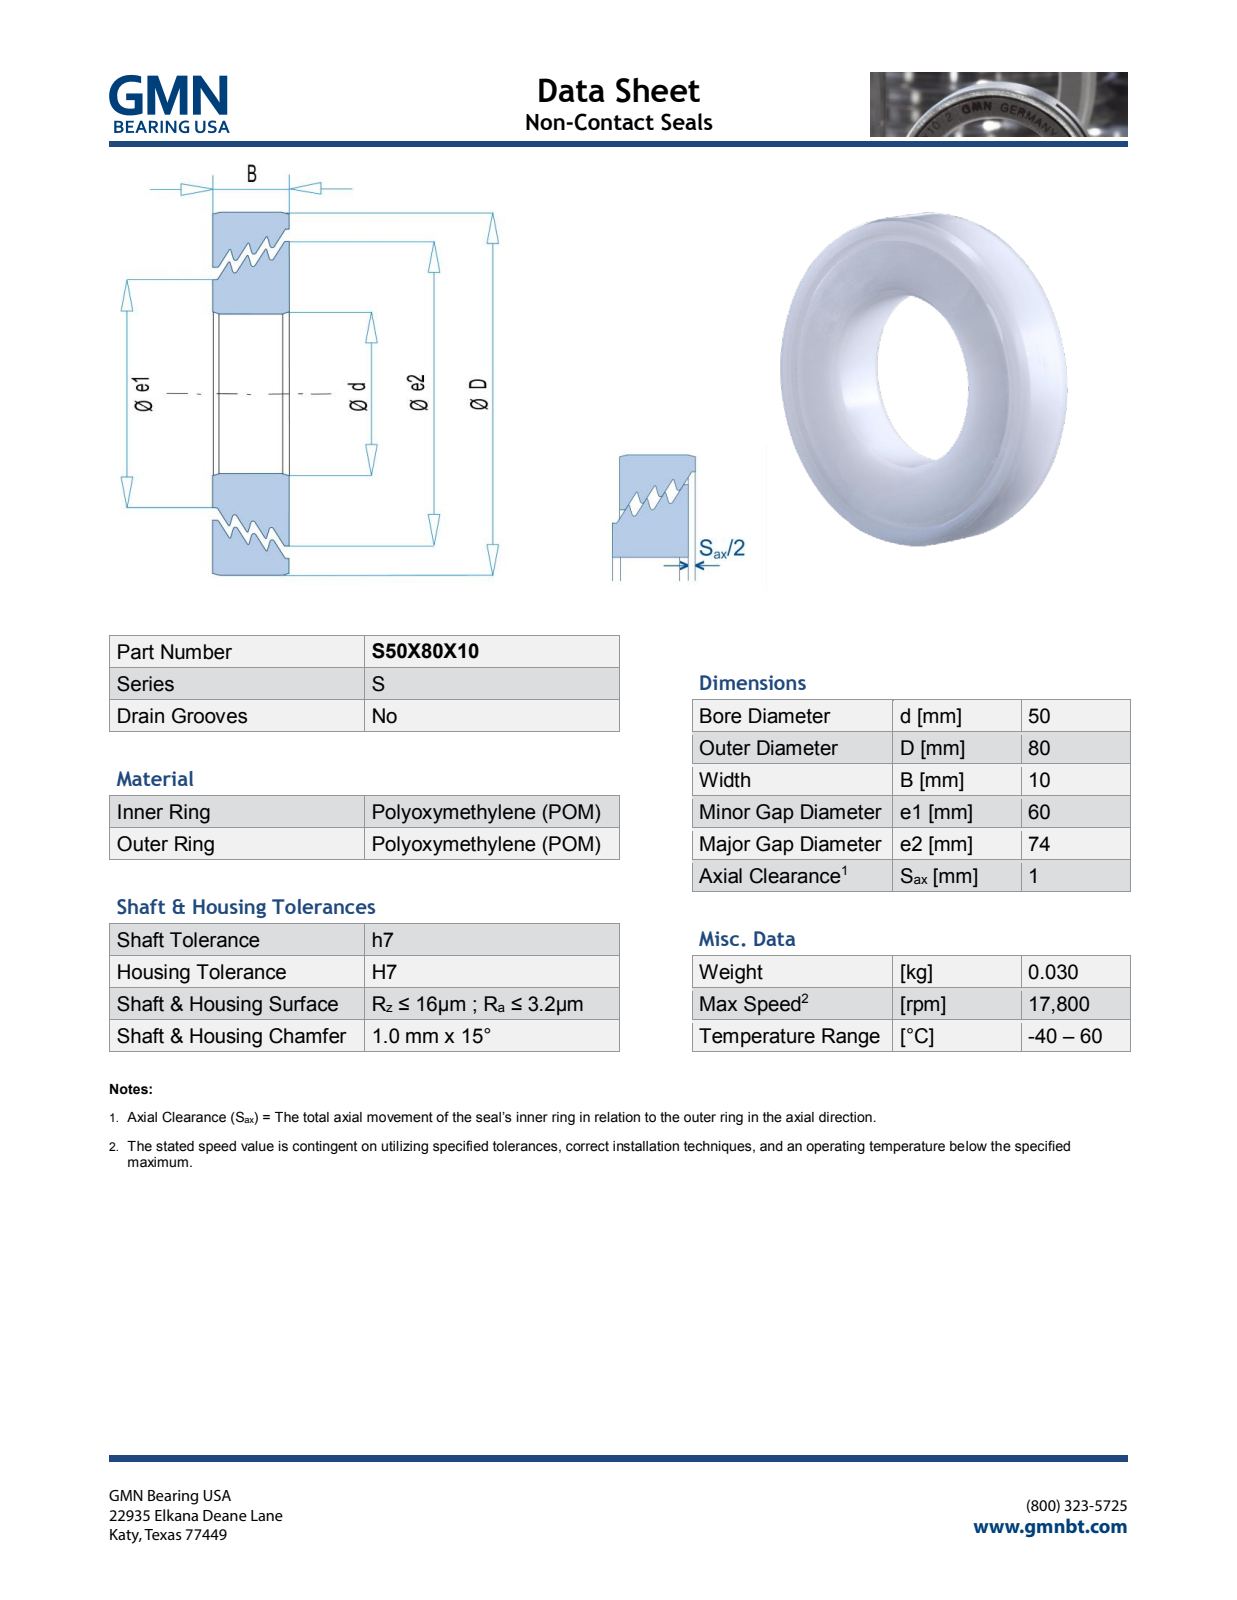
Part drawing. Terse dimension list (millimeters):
name: S50X80X10_PRT
written by: PRO/ENGINEER BY PARAMETRIC TECHNOLOGY CORPORATION, 2013150 (AUTOMOTIVE_DESIGN)
unit: mm
bodies: 2 solids, 695 faces (615 planar, 12 cylindrical, 68 other)
size: 80 × 80 × 10.07
volume: 28 788 mm³; area: 18 205 mm²
holes: 1× ⌀50, 1× ⌀61.63, 1× ⌀75.63
bosses: 1× ⌀80, 1× ⌀74, 1× ⌀60
face distances: 10, 10.07, 0.42, 3.33, 0.41, 2.91, 2.36, 0.35, 2.5, 1.49
